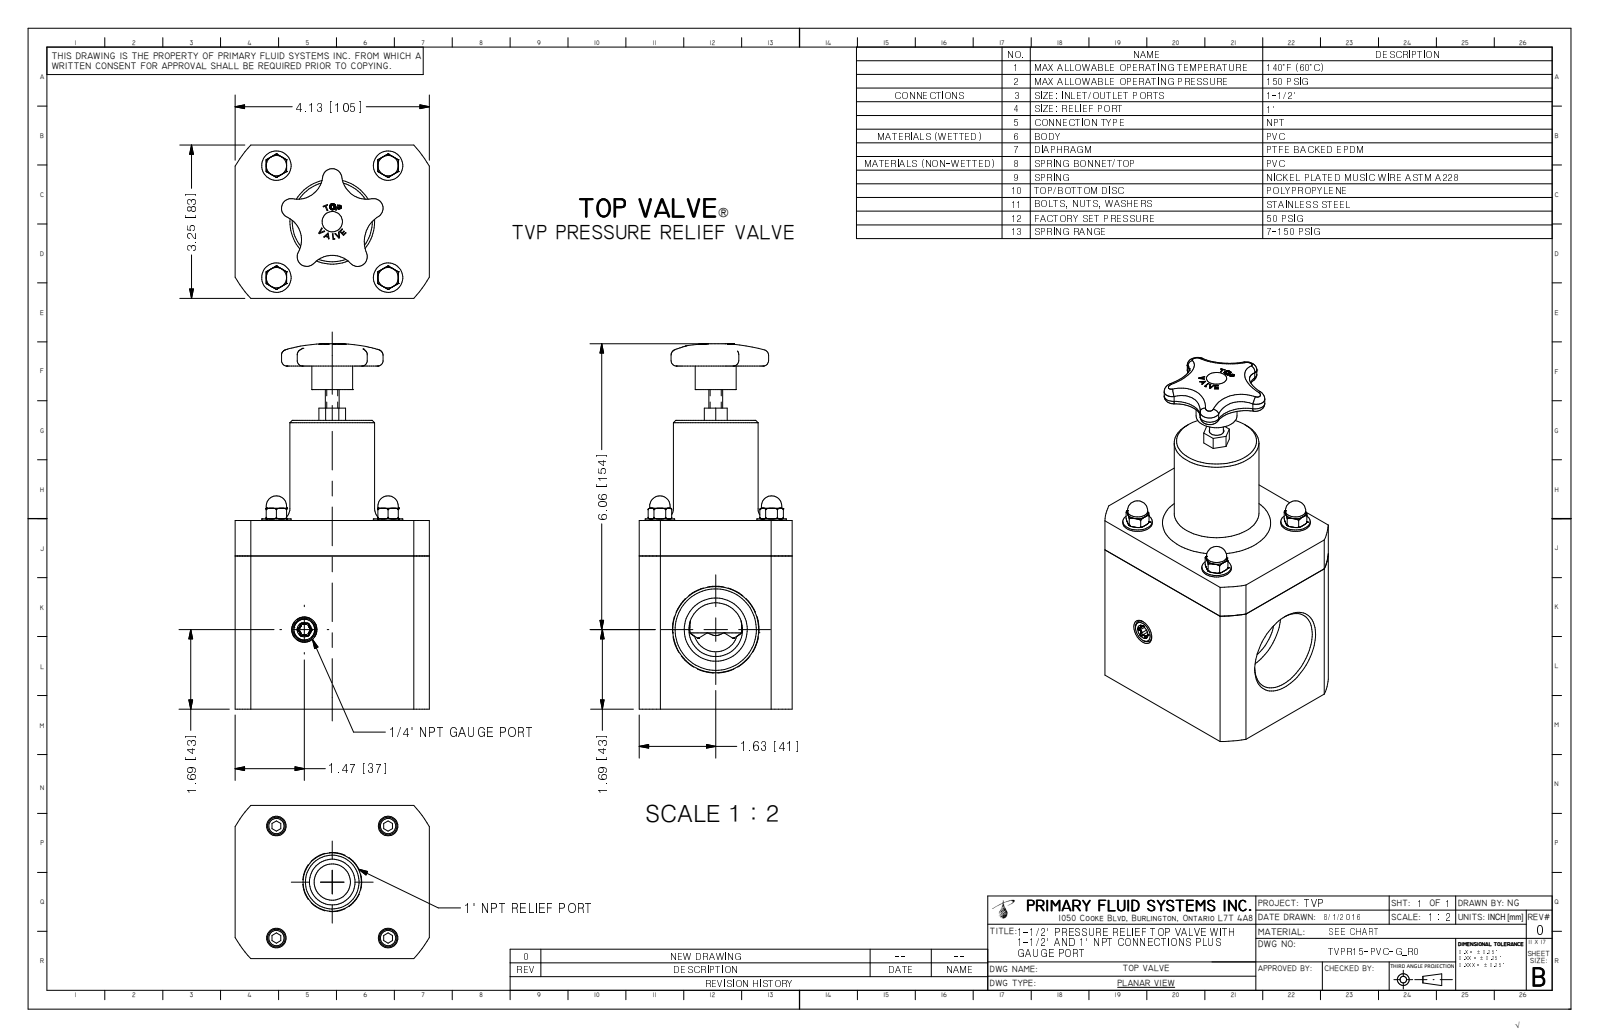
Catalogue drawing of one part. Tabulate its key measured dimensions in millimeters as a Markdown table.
| quantity | value |
| --- | --- |
| part name | TVPR15-PVC-G_R0 |
| STEP written by | Autodesk Inventor 2009 (AUTOMOTIVE_DESIGN) |
| units | millimeters |
| bodies | 1 solid, 362 faces (153 planar, 52 cylindrical, 157 other) |
| overall size | 196.9 × 104.8 × 82.6 |
| volume | 884 100 mm³ |
| surface area | 79 230 mm² |
| round holes (diameter × count) | 4.4 × 4, 29 × 1, 43.9 × 1 |
| round bosses / shafts (diameter × count) | 15.9 × 4, 11 × 4, 9.5 × 4, 45.7 × 1, 22.1 × 1, 7.4 × 1 |
| partial cylindrical surfaces (radius × count) | 0.7 × 6, 2.2 × 5, 5.2 × 5, 13.6 × 4, 16.7 × 4, 15.9 × 1, 18.9 × 1, 60.3 × 1 |
| main face-to-face distances | 82.6, 101.6, 104.8, 25.4, 79.4, 54, 155.6, 20.3, 81.3, 135.3 |
| hole center spacings | 42.6, 42.7, 60.3, 60.3, 85.3 |
